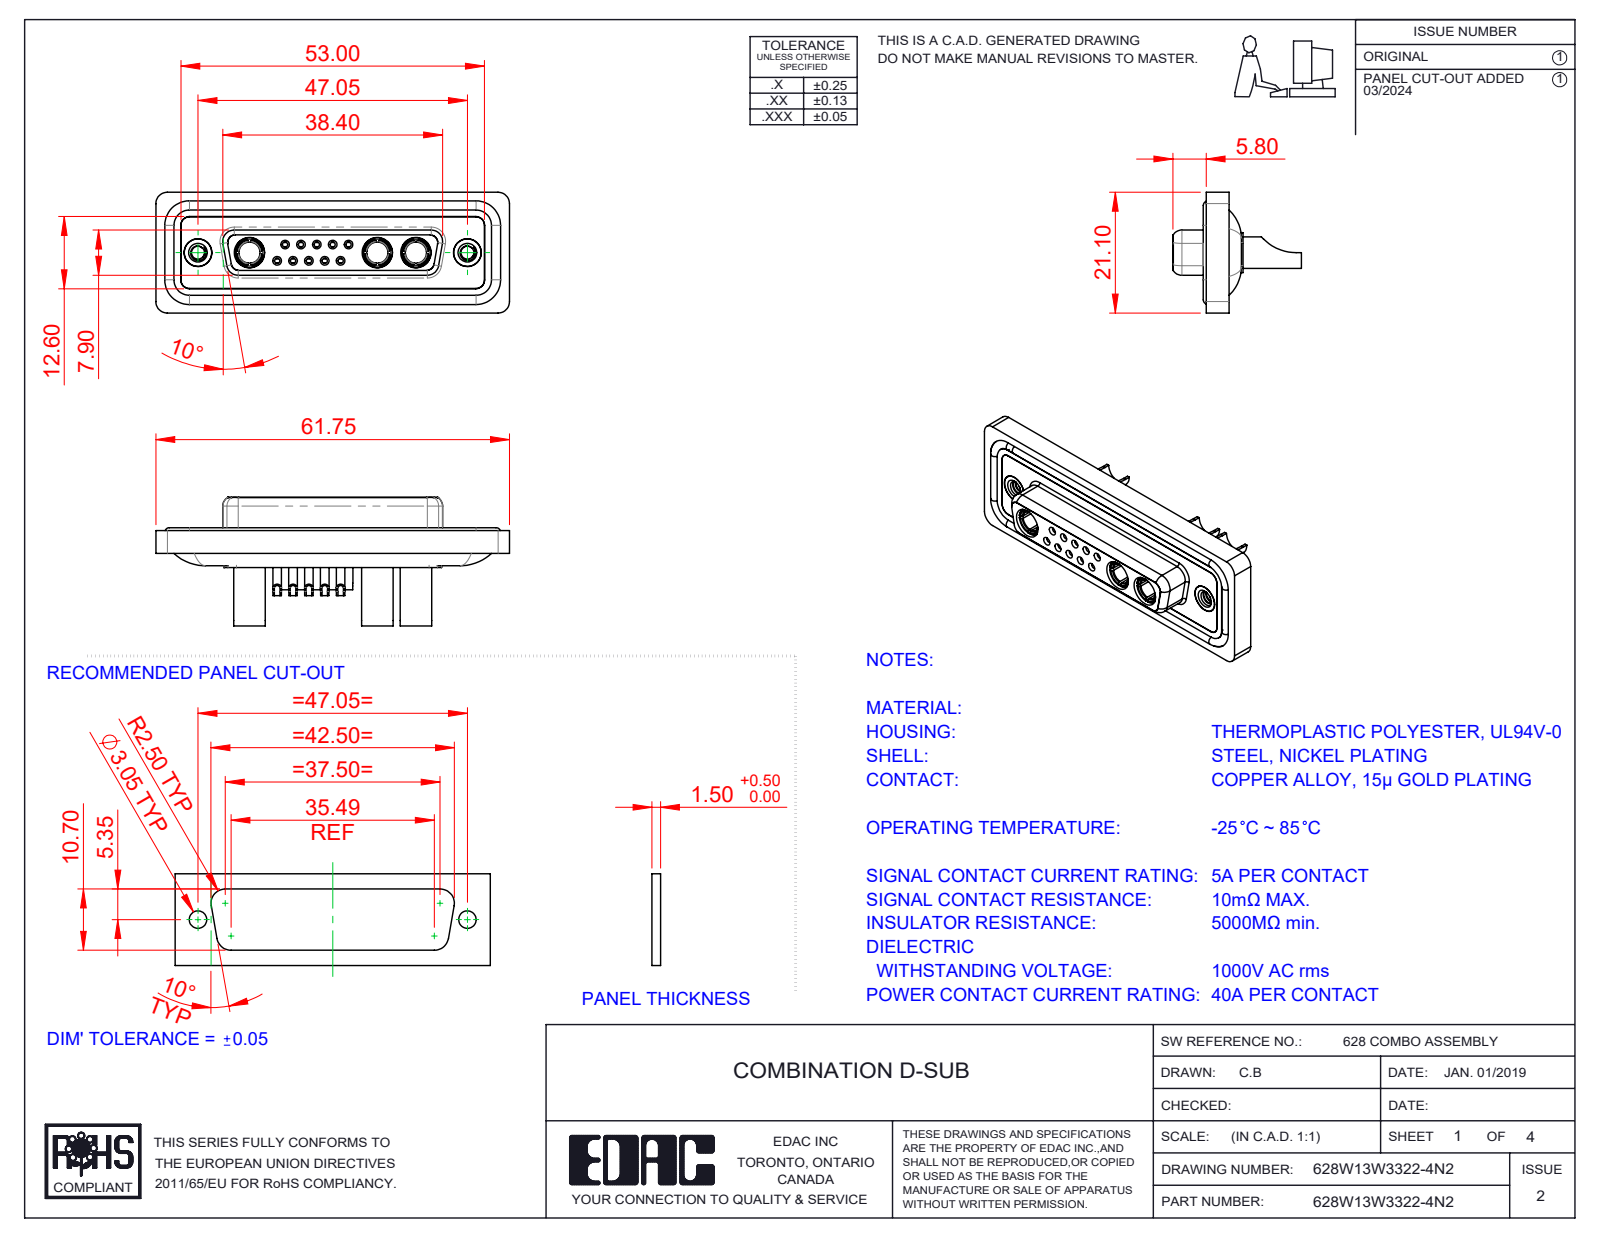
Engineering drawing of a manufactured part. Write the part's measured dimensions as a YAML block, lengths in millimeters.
part_name: "628W13W3322-4N2; 628Combo Shell Rear_25 Contacts; 628Combo Housing_13W3; 628Combo Threaded Rivet_2 (+5 more)"
step_written_by: "SolidWorks 2023 (CONFIG_CONTROL_DESIGN)"
units: millimeters
bodies: {solids: 23, faces: 1167, planar: 368, cylindrical: 470, other: 329}
overall_size: [61.75, 22.45, 21.1]
volume: 8413
surface_area: 14233
round_holes:
  - {diameter: 0.9, count: 10}
  - {diameter: 1, count: 10}
  - {diameter: 1.1, count: 10}
  - {diameter: 1.5, count: 10}
  - {diameter: 2, count: 10}
  - {diameter: 1.6, count: 5}
  - {diameter: 1.7, count: 5}
  - {diameter: 4.85, count: 5}
  - {diameter: 3.7, count: 3}
  - {diameter: 4.6, count: 3}
  - {diameter: 5.3, count: 3}
  - {diameter: 2.26, count: 2}
round_bosses_or_shafts:
  - {diameter: 2.2, count: 10}
  - {diameter: 1.6, count: 9}
  - {diameter: 5.5, count: 3}
  - {diameter: 5.2, count: 3}
  - {diameter: 4.96, count: 3}
  - {diameter: 4.75, count: 3}
  - {diameter: 3.75, count: 3}
  - {diameter: 4.95, count: 2}
partial_cylinders:
  - {radius: 1.5, count: 22}
  - {radius: 2, count: 18}
  - {radius: 1.35, count: 8}
  - {radius: 1.6, count: 8}
  - {radius: 1, count: 6}
  - {radius: 0.25, count: 4}
  - {radius: 0.5, count: 4}
  - {radius: 0.6, count: 4}
face_to_face_distances: [0.4, 7.45, 1.8, 5.65, 0.5, 6.6, 7.05, 1.6, 2.9, 1.1]
hole_center_spacings: [3.16, 2.77, 5.03, 5.04, 5.54, 8.31, 7.49, 2.76]
